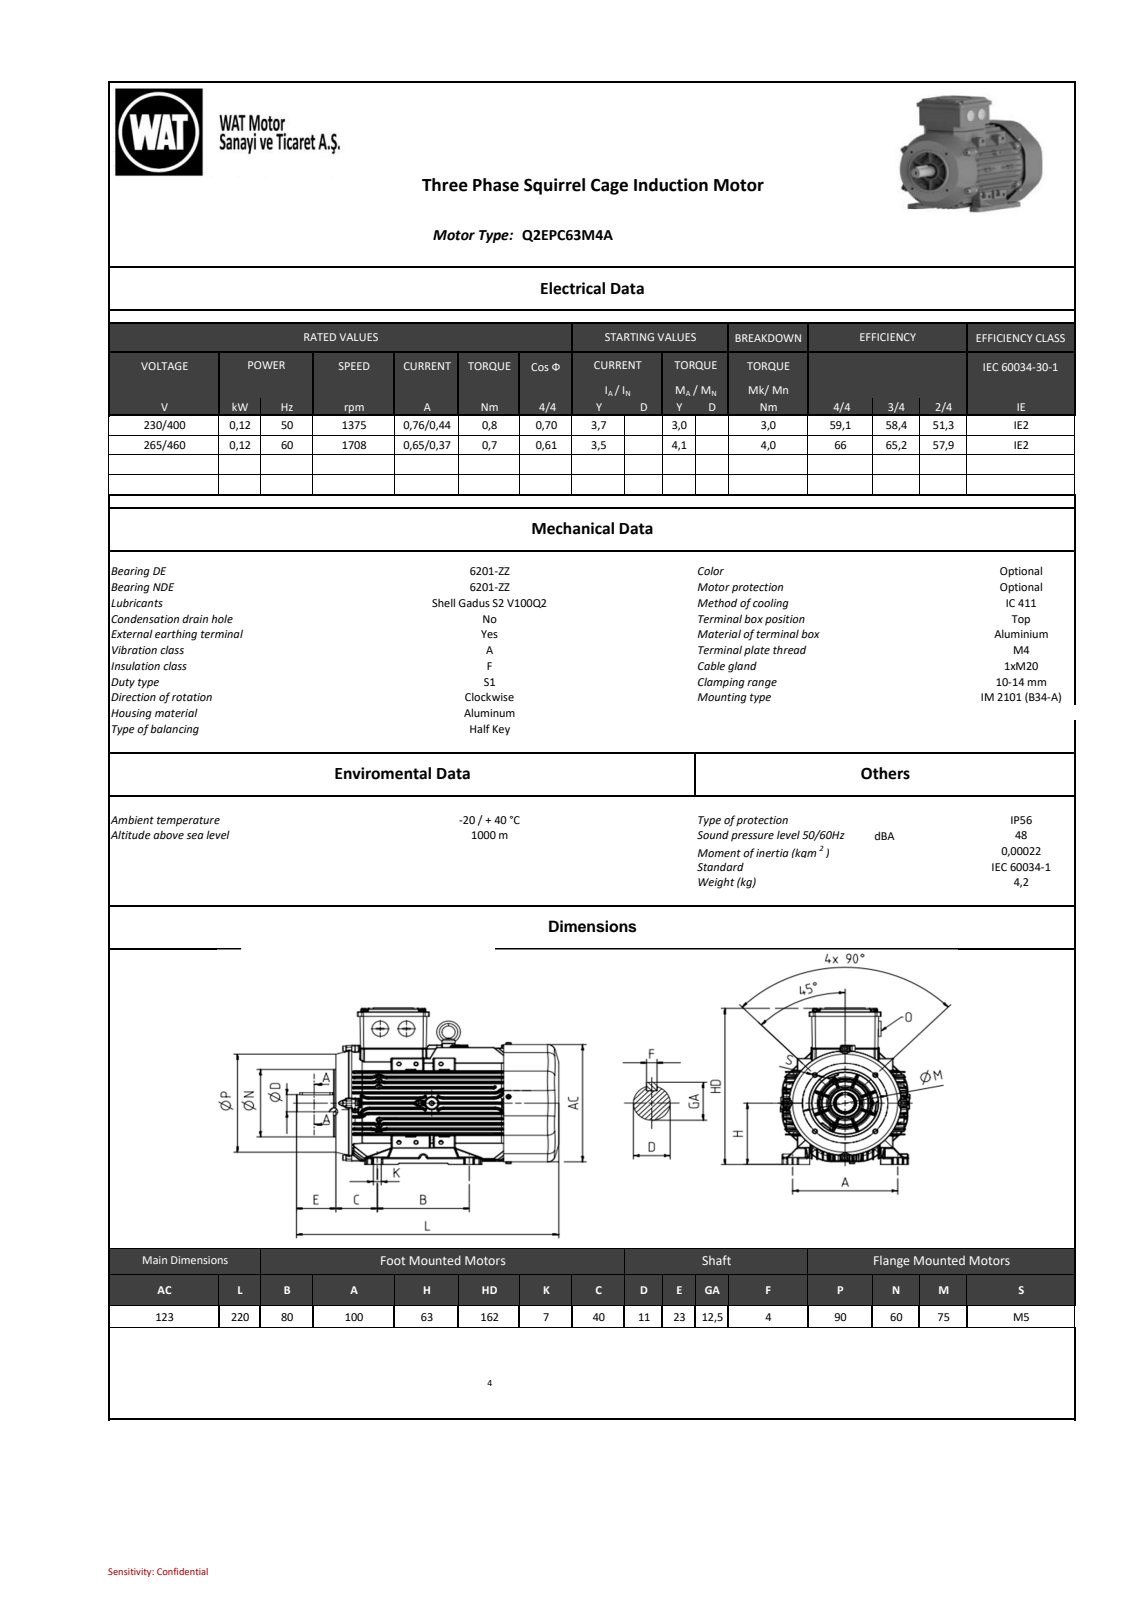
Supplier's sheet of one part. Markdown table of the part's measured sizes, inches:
| quantity | value |
| --- | --- |
| part name | QS63PCGMM |
| STEP written by | UNIX (AUTOMOTIVE_DESIGN) |
| units | inches |
| bodies | 5 solids, 2855 faces (0 planar, 0 cylindrical, 2855 other) |
| overall size | 8.64 × 6.343 × 5.039 |
| volume | 2.767 in³ |
| surface area | 612.9 in² |
